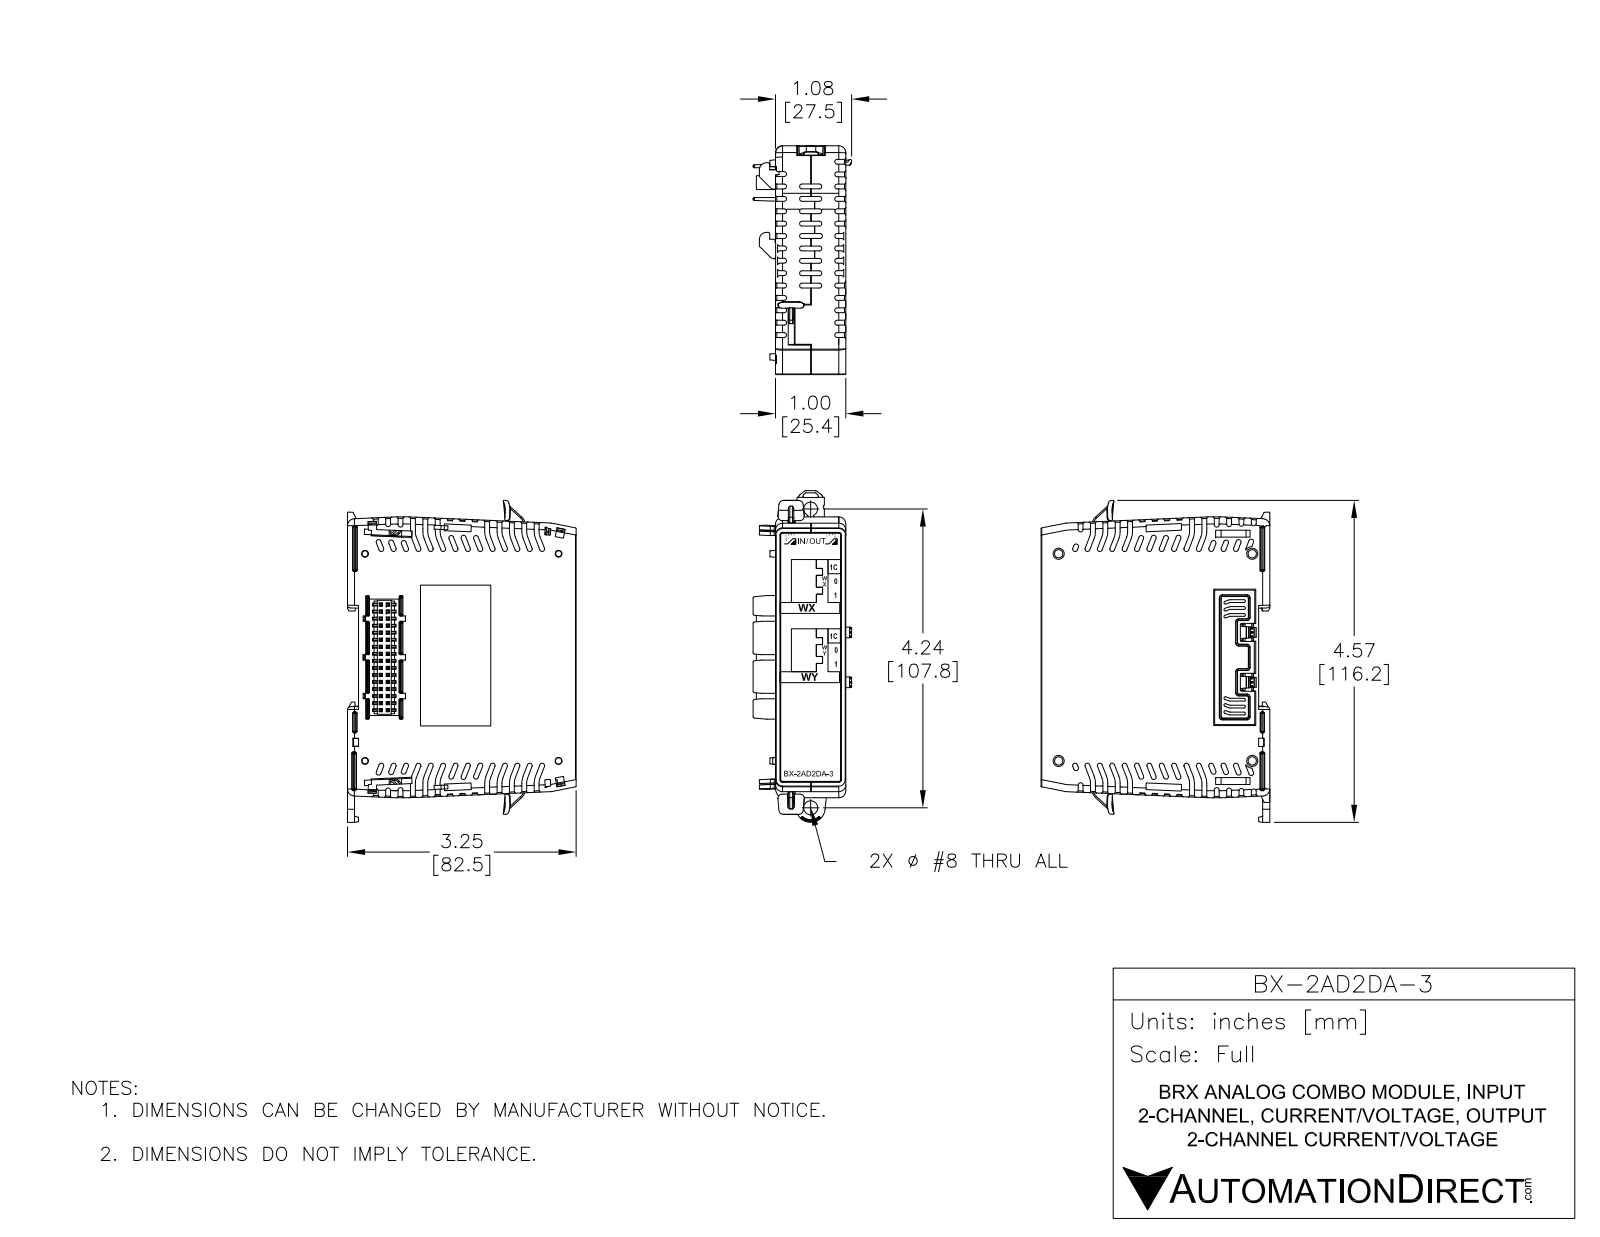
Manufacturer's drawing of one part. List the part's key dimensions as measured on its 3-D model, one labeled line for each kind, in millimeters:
Part name (STEP PRODUCT): BX-2AD2DA-3
STEP written by: SolidWorks 2017 (AUTOMOTIVE_DESIGN)
Units: millimetres
Bodies: 5 solids, 3626 faces (2589 planar, 579 cylindrical, 458 other)
Overall size (bounding box): 116.5 × 82.6 × 35.6
Volume: 189 800 mm³ · Surface area: 47 030 mm²
Round holes (diameter × count): ⌀1.2 ×2, ⌀1.7 ×2, ⌀3 ×2, ⌀3 ×2, ⌀5.1 ×1
Round bosses / shafts (diameter × count): ⌀1.6 ×2, ⌀1.5 ×2
Partial cylindrical surfaces — rounded edges, fillets, slot ends (radius × count): R0.1 ×102, R0.3 ×47, R0.2 ×45, R0.5 ×34, R0.1 ×24, R3 ×14, R1 ×13, R0.3 ×12
Main face-to-face distances: 25.4, 81.6, 81.8, 12.1, 4, 77.5, 77.8, 2.5, 1, 20
Hole centre spacings: 2.5, 20.9, 23.3, 33, 53.2, 55.7, 65.7, 66.5
